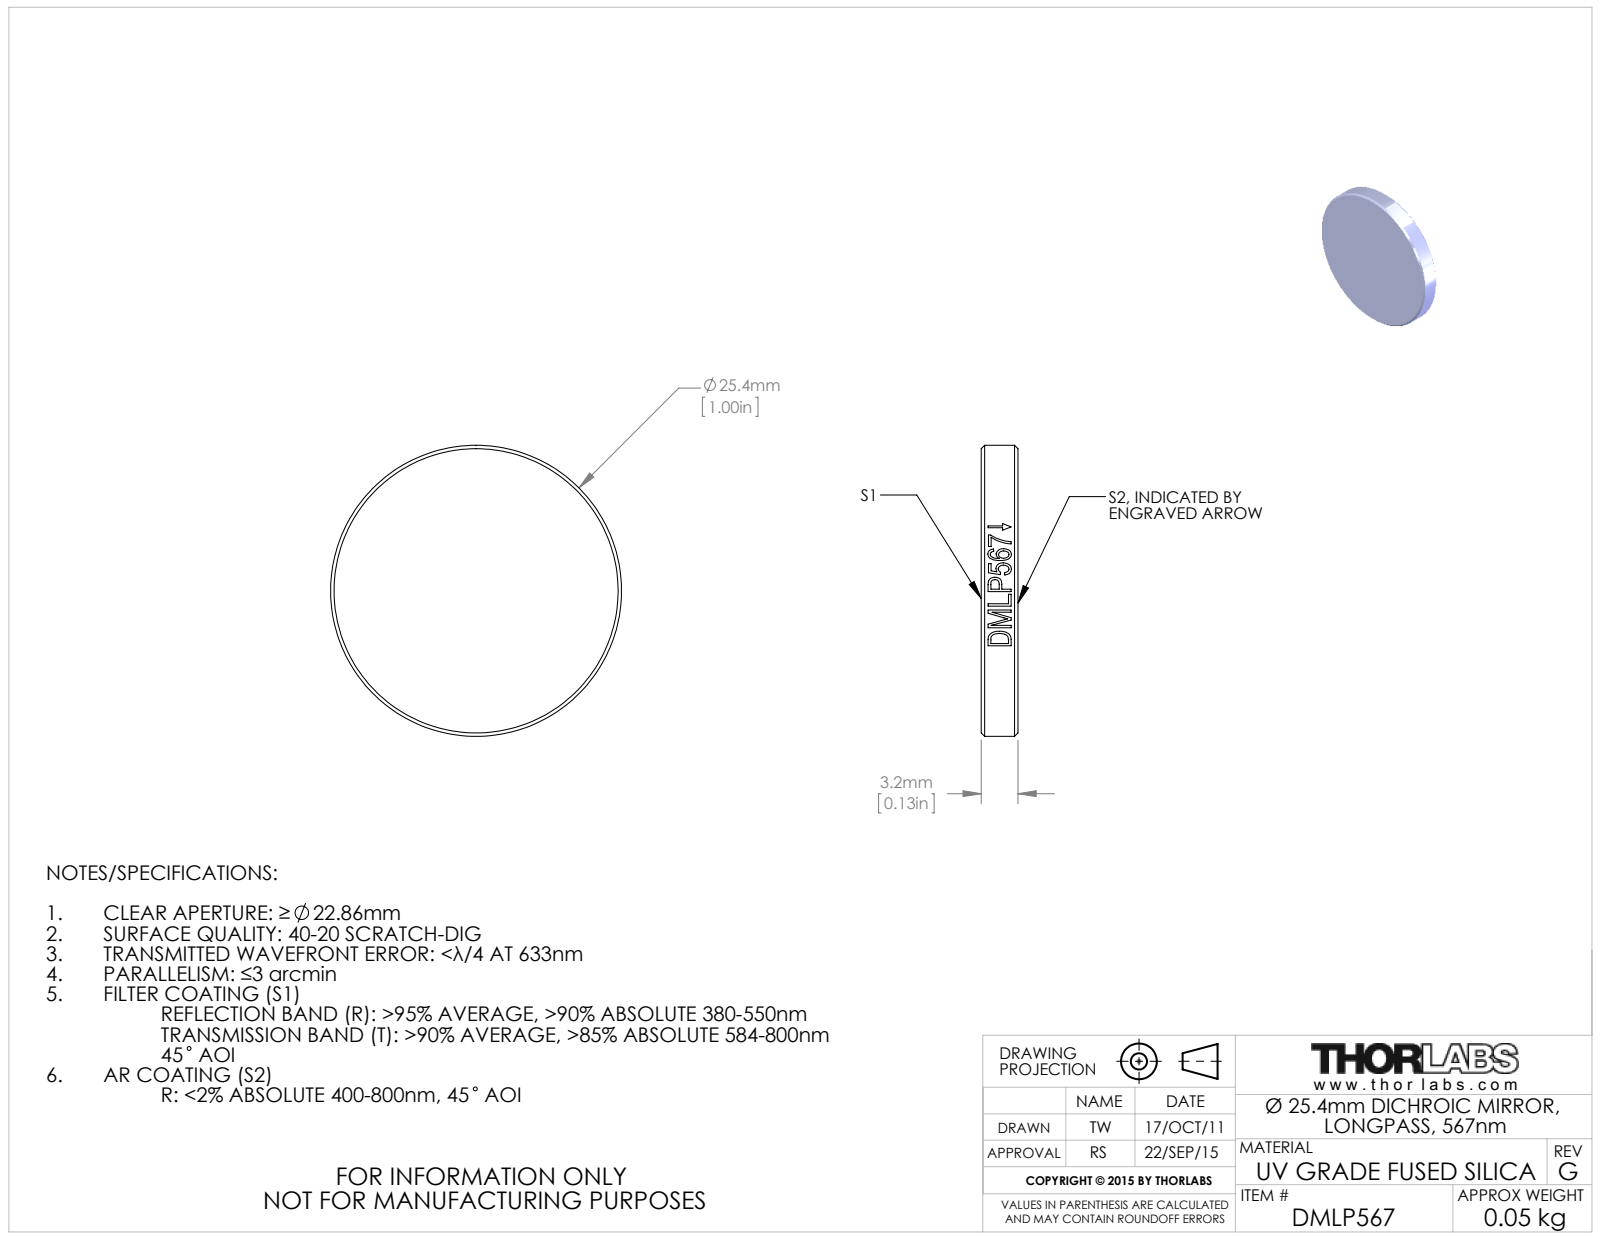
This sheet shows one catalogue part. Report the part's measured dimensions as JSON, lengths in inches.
{"part_name": "18096-E0W", "step_written_by": "SolidWorks 2011 (CONFIG_CONTROL_DESIGN)", "units": "inches", "bodies": {"solids": 0, "faces": 19, "planar": 2, "cylindrical": 13, "other": 4}, "overall_size": [1, 1, 0.126], "round_bosses_or_shafts": [[1, 1]], "face_to_face_distances": [0.126]}
